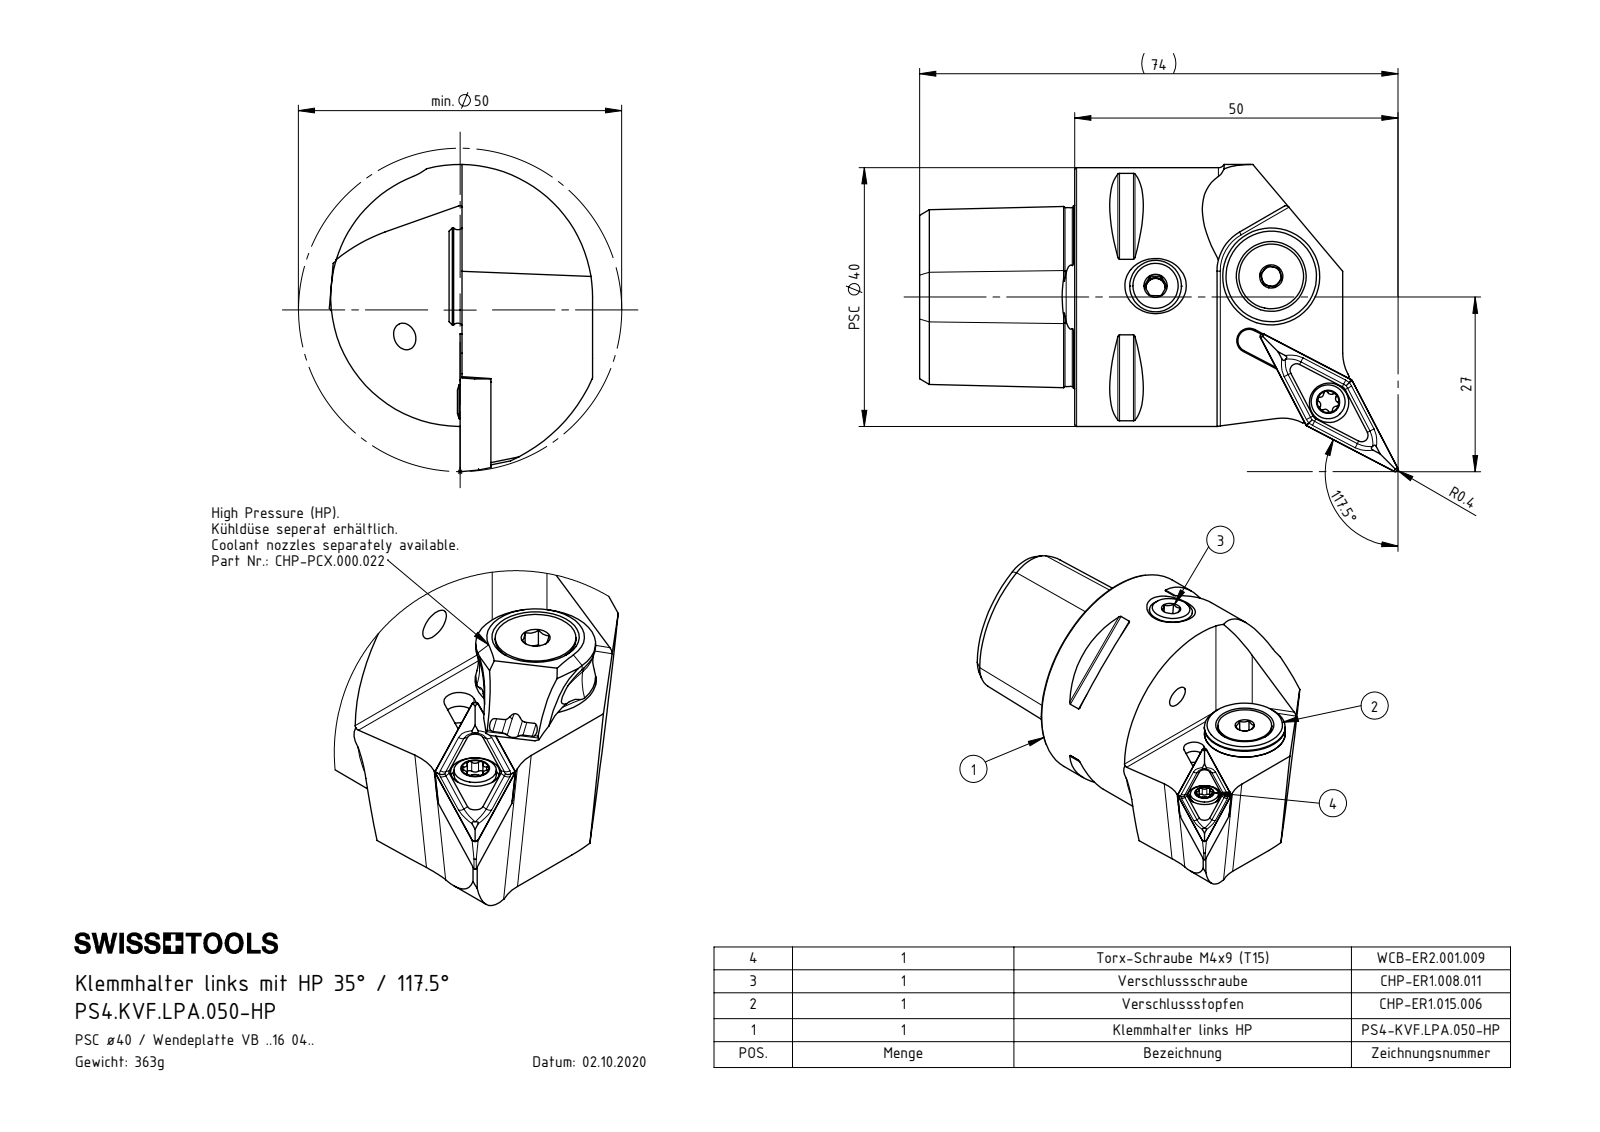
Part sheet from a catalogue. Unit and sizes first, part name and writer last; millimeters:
Units: millimetres
Overall size (bounding box): 74 × 47.5 × 40.73
Round holes (diameter × count): ⌀3.3 ×2, ⌀4.2 ×2, ⌀1.2 ×1, ⌀2 ×1, ⌀2.5 ×1, ⌀3 ×1, ⌀4 ×1, ⌀4.4 ×1, ⌀4.6 ×1, ⌀5 ×1, ⌀5.2 ×1, ⌀6.1 ×1
Round bosses / shafts (diameter × count): ⌀40 ×1, ⌀15 ×1, ⌀13.4 ×1, ⌀10 ×1, ⌀8 ×1, ⌀5.5 ×1, ⌀5.25 ×1, ⌀5 ×1
Partial cylindrical surfaces — rounded edges, fillets, slot ends (radius × count): R0.3 ×8, R0.34 ×6, R0.59 ×6, R7 ×3, R0.15 ×2, R0.5 ×2, R1.75 ×1, R3 ×1
Main face-to-face distances: 22, 4.46, 4.5, 15.7, 15.74, 20.2, 24, 46, 15.52, 22.2
Hole centre spacings: 4.5, 18.55, 18.66, 18.73, 21.28, 21.48, 22.74, 23.5
Volume: 45 697 mm³ · Surface area: 15 224 mm²
Bodies: 8 solids, 400 faces (96 planar, 107 cylindrical, 197 other)
Part name (STEP PRODUCT): DIN 3771 - 13x1; WCB-ER2.001.009_A; CHP-ER1.008.011_A; VBMT160404 (+6 more)
STEP written by: SolidWorks 2017 (AUTOMOTIVE_DESIGN)
